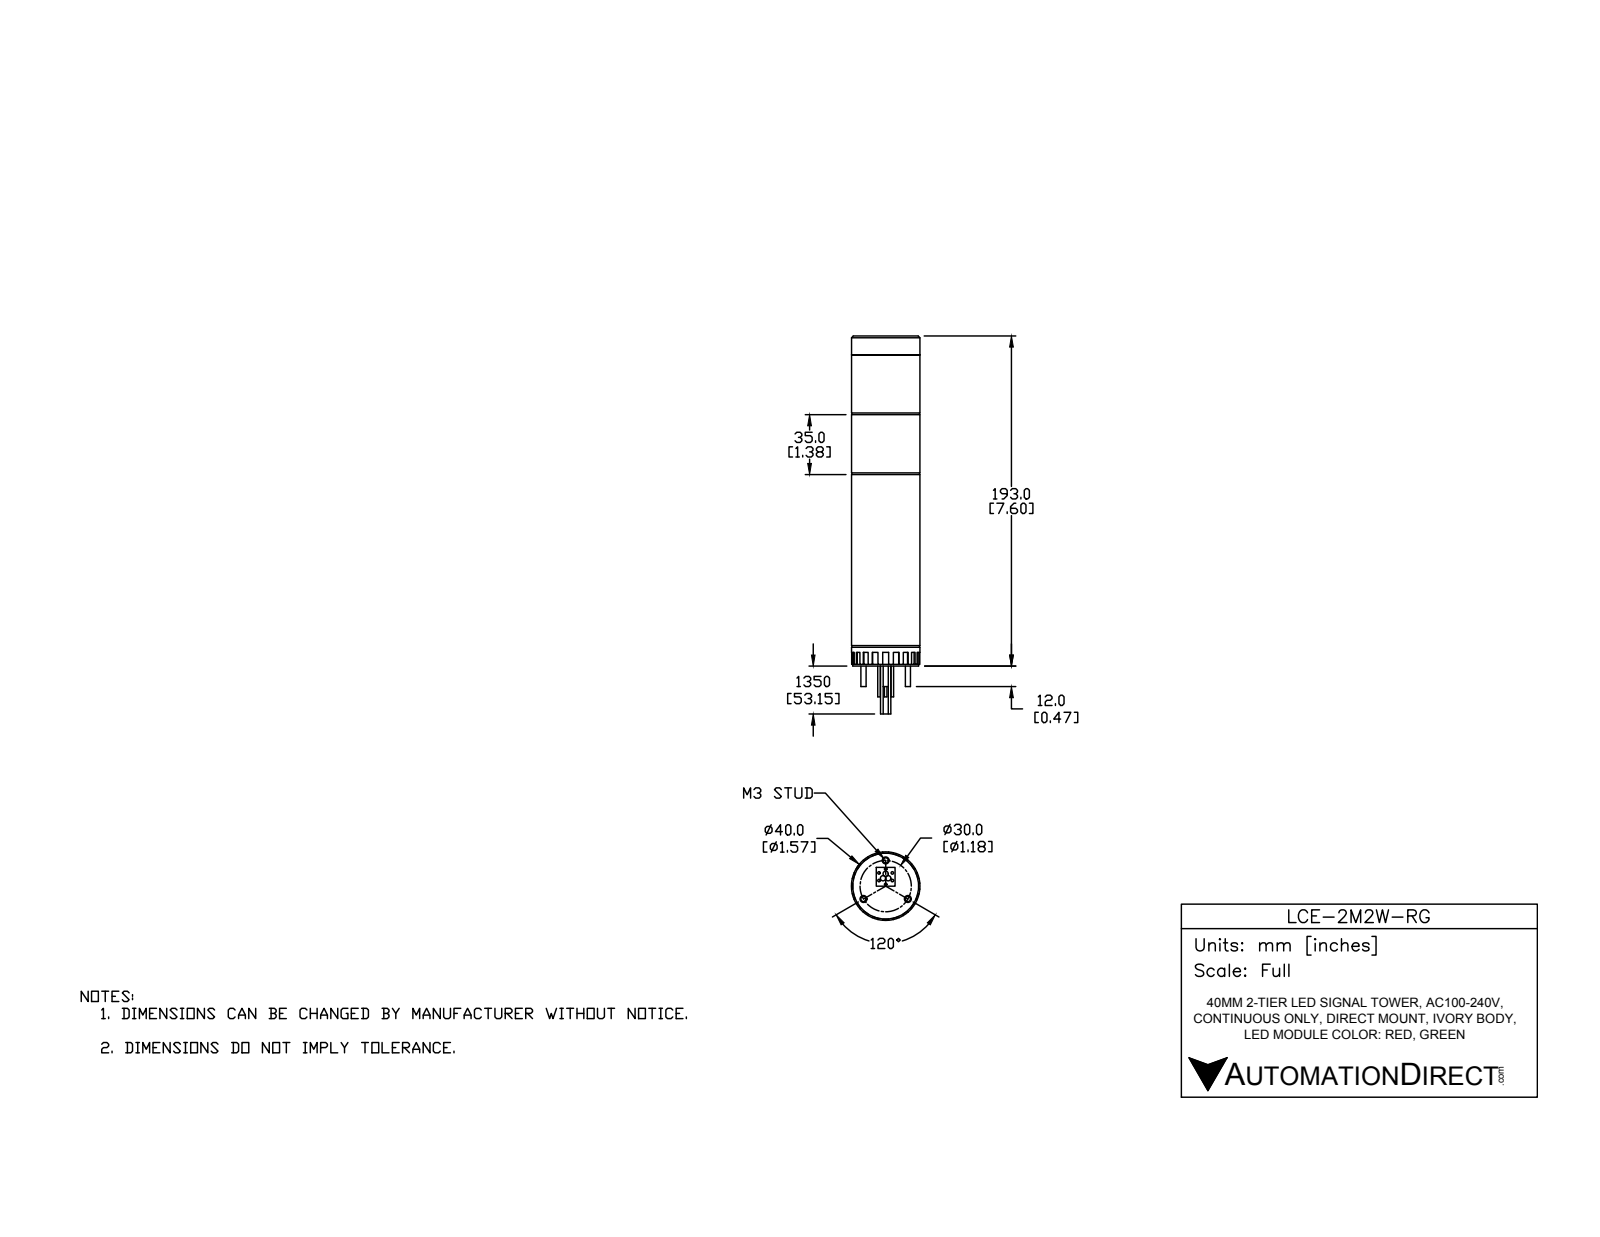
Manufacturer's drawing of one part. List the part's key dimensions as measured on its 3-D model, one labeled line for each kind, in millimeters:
Part name (STEP PRODUCT): LCE-2M2W-RG
STEP written by: SolidWorks 2016 (AUTOMOTIVE_DESIGN)
Units: millimetres
Bodies: 22 solids, 206 faces (150 planar, 52 cylindrical, 4 other)
Overall size (bounding box): 221 × 40 × 40
Volume: 241 786 mm³ · Surface area: 48 959 mm²
Round holes (diameter × count): ⌀4 ×3, ⌀8 ×1
Round bosses / shafts (diameter × count): ⌀3 ×6, ⌀1.5 ×6, ⌀40 ×1, ⌀39.5 ×1, ⌀38.5 ×1, ⌀5.5 ×1
Main face-to-face distances: 1, 35, 34, 101, 136, 11, 181, 112, 147, 36
Hole centre spacings: 15, 25.98
